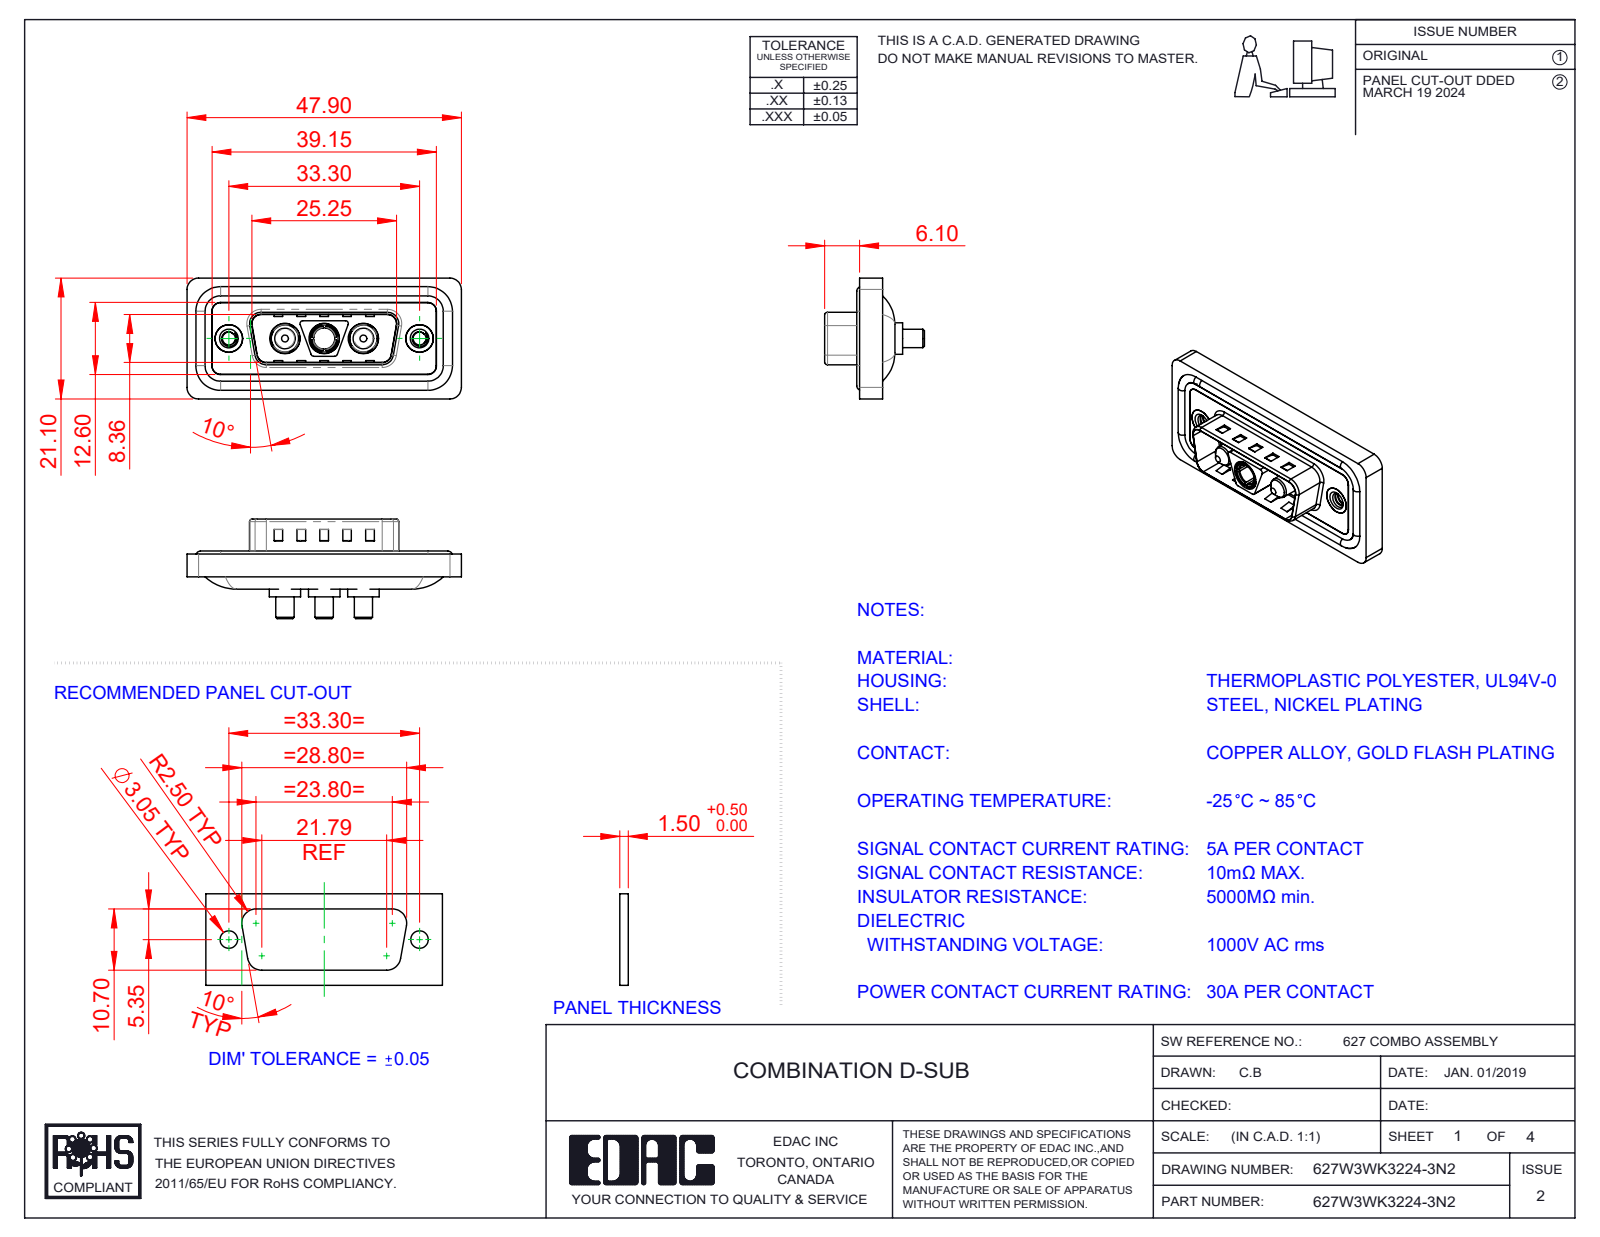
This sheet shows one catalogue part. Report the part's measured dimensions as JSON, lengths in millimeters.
{"part_name": "Power Pin_30A S; 627Combo Housing_3WK3; 627Combo Shell Rear_15 Contacts; Power Socket_30A S (+4 more)", "step_written_by": "SolidWorks 2023 (CONFIG_CONTROL_DESIGN)", "units": "millimeters", "bodies": {"solids": 13, "faces": 609, "planar": 231, "cylindrical": 250, "other": 128}, "overall_size": [47.9, 21.1, 17.4], "volume_mm3": 5709, "surface_area_mm2": 9141, "round_holes": [[4.85, 3], [5.3, 3], [2.26, 2], [4, 2], [4.8, 2], [5, 2], [3.7, 1]], "round_bosses_or_shafts": [[1.6, 4], [5.5, 3], [5.2, 3], [4.75, 3], [3.75, 3], [3.2, 3], [4.9, 2], [3.6, 2]], "partial_cylinders_radius": [[1.5, 26], [2, 20], [0.5, 12], [1.6, 8], [0.25, 4], [0.6, 4], [0.65, 4], [0.9, 4]], "face_to_face_distances": [0.4, 1.1, 1.5, 0.5, 1.6, 3.1, 2.9, 4, 0.82, 9.58], "hole_center_spacings": [6.85, 9.8, 16.65, 23.5, 13.7, 33.3]}
